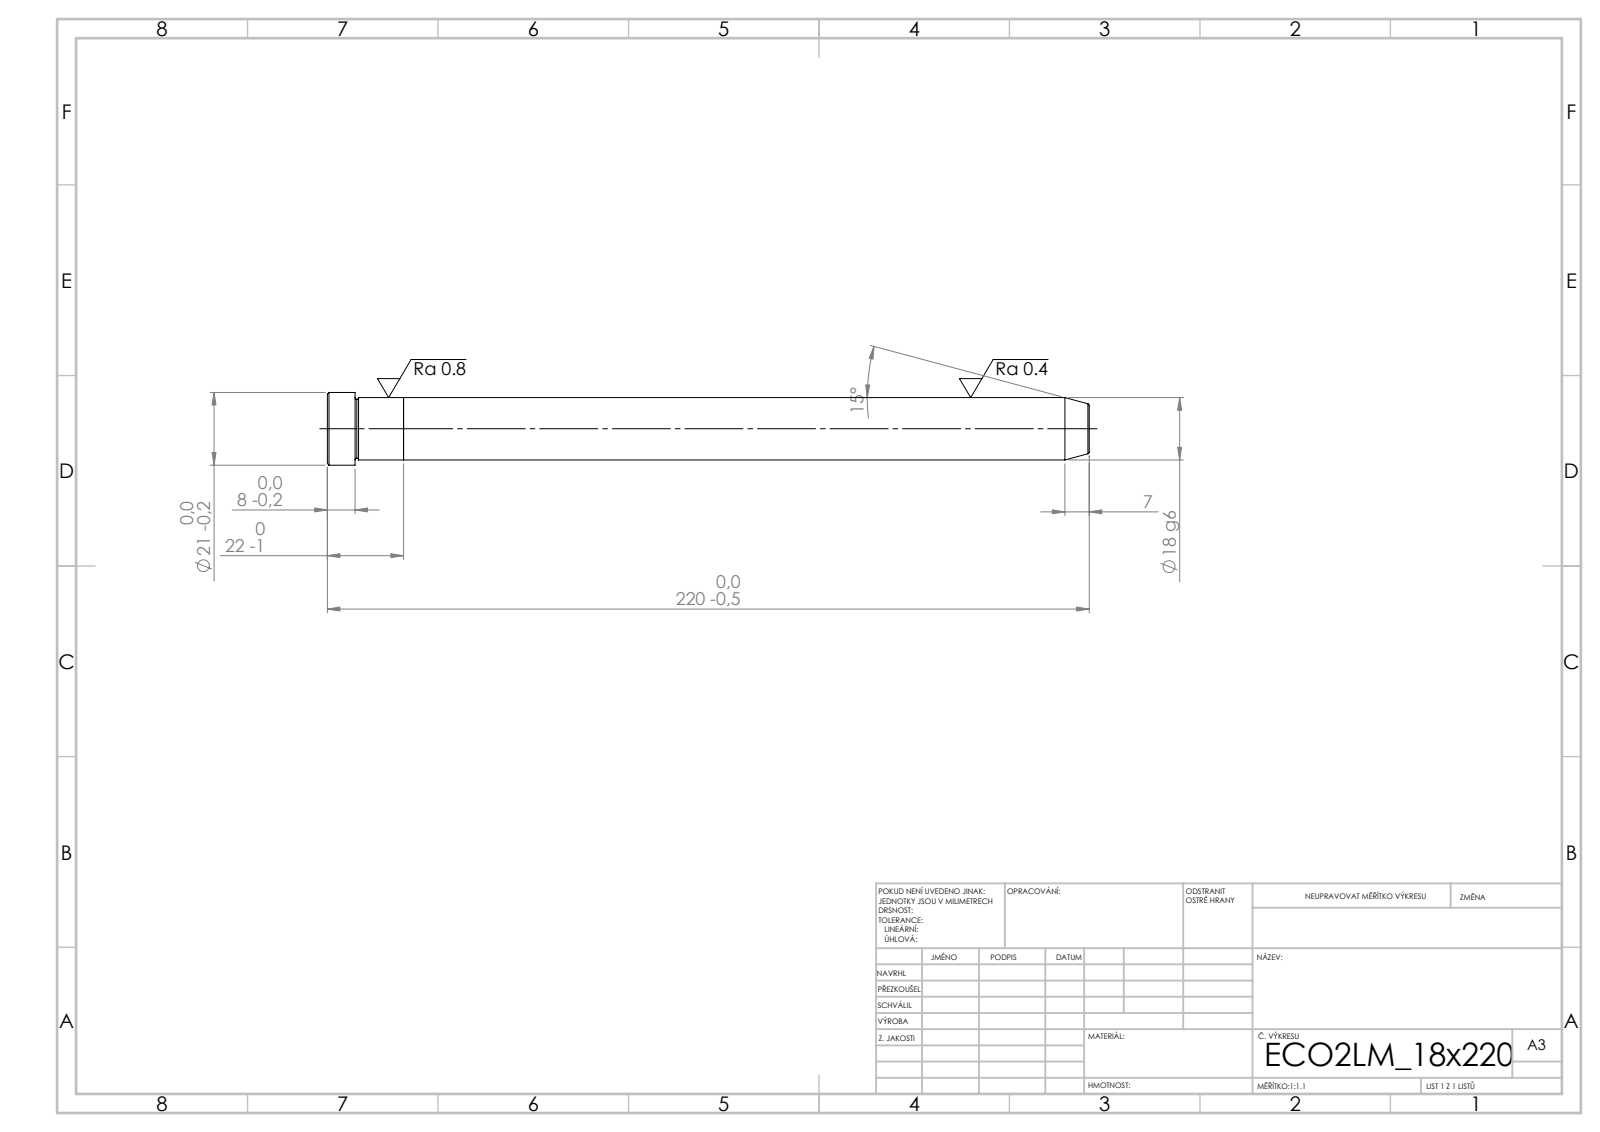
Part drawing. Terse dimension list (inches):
written by: SolidWorks 2019 (CONFIG_CONTROL_DESIGN)
unit: in
bodies: 2 solids, 21 faces (5 planar, 6 cylindrical, 10 other)
size: 8.661 × 0.827 × 0.827
volume: 3.438 in³; area: 21.08 in²
bosses: 1× ⌀0.827, 1× ⌀0.709
face distances: 0.866, 7.795, 8.661, 8.346, 0.551, 0.315
